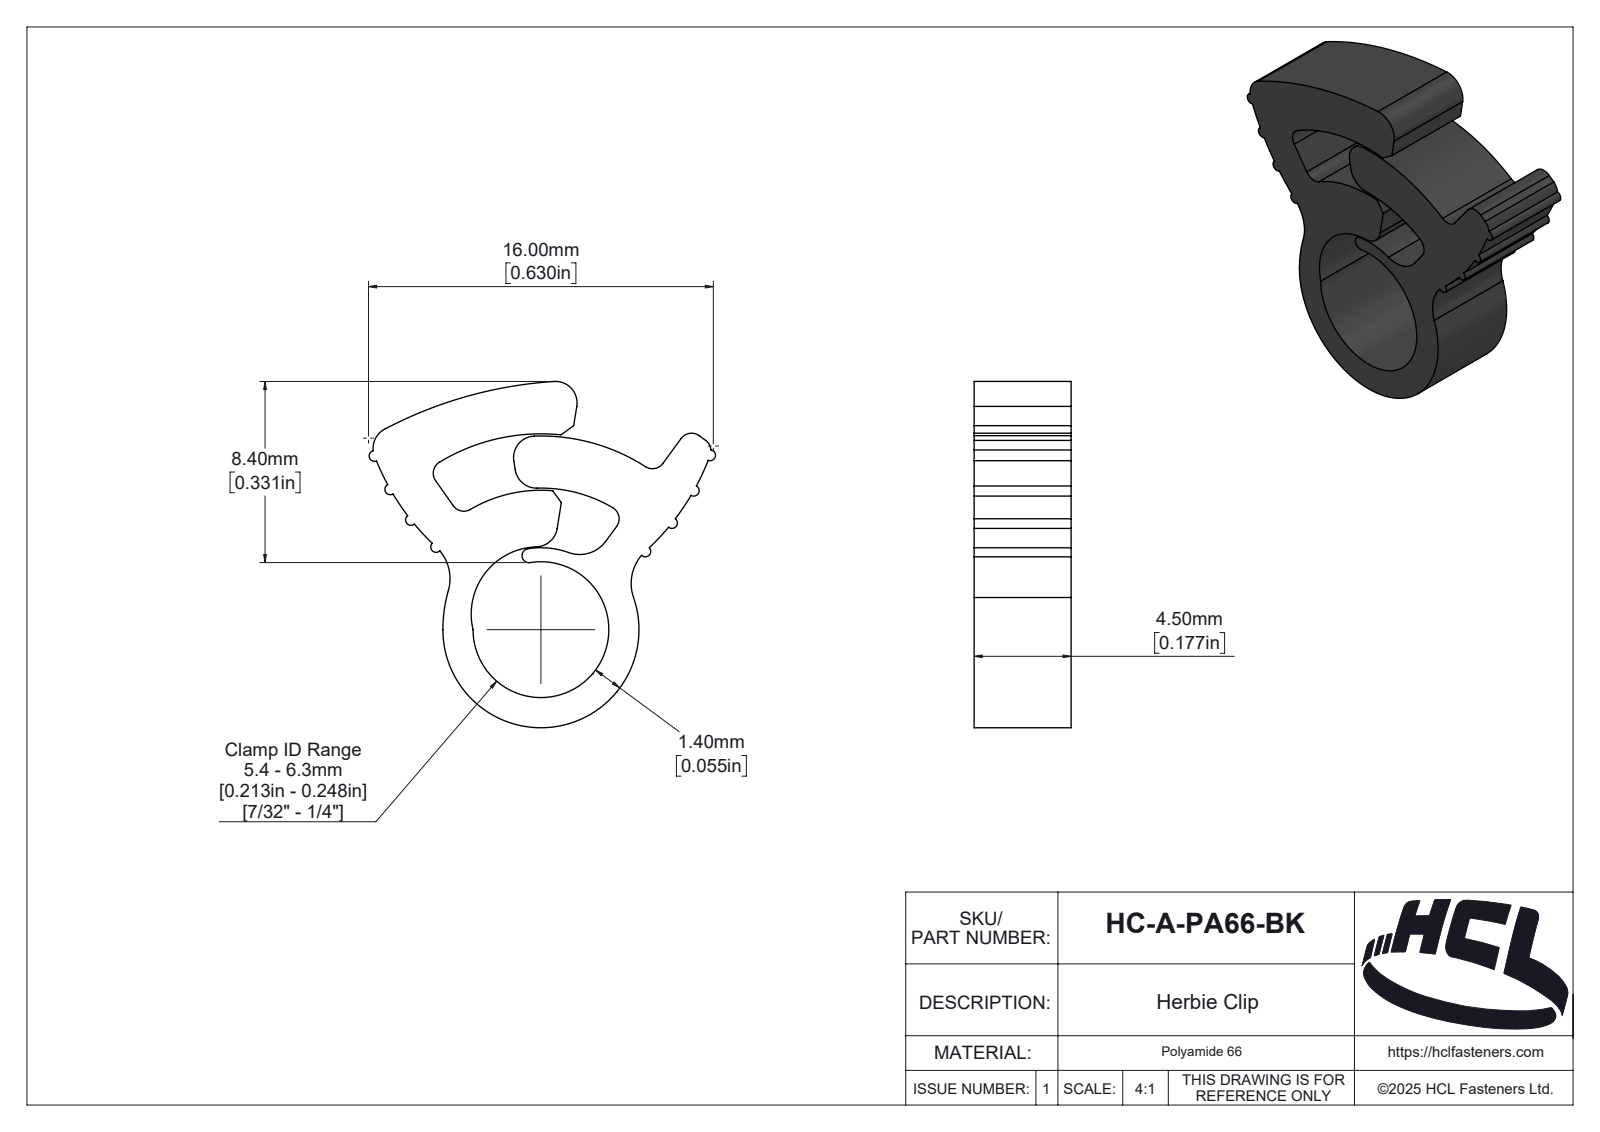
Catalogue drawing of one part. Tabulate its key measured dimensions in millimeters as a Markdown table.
| quantity | value |
| --- | --- |
| part name | HC-A-PA66-BK |
| STEP written by | SolidWorks 2025 (AUTOMOTIVE_DESIGN) |
| units | millimeters |
| bodies | 1 solid, 162 faces (13 planar, 100 cylindrical, 49 other) |
| overall size | 16.07 × 16.06 × 4.5 |
| volume | 447 mm³ |
| surface area | 694 mm² |
| partial cylindrical surfaces (radius × count) | 0.25 × 8, 0.6 × 6, 1 × 5, 2 × 2, 0.17 × 1, 0.33 × 1, 0.67 × 1, 0.84 × 1 |
| main face-to-face distances | 4.5 |
